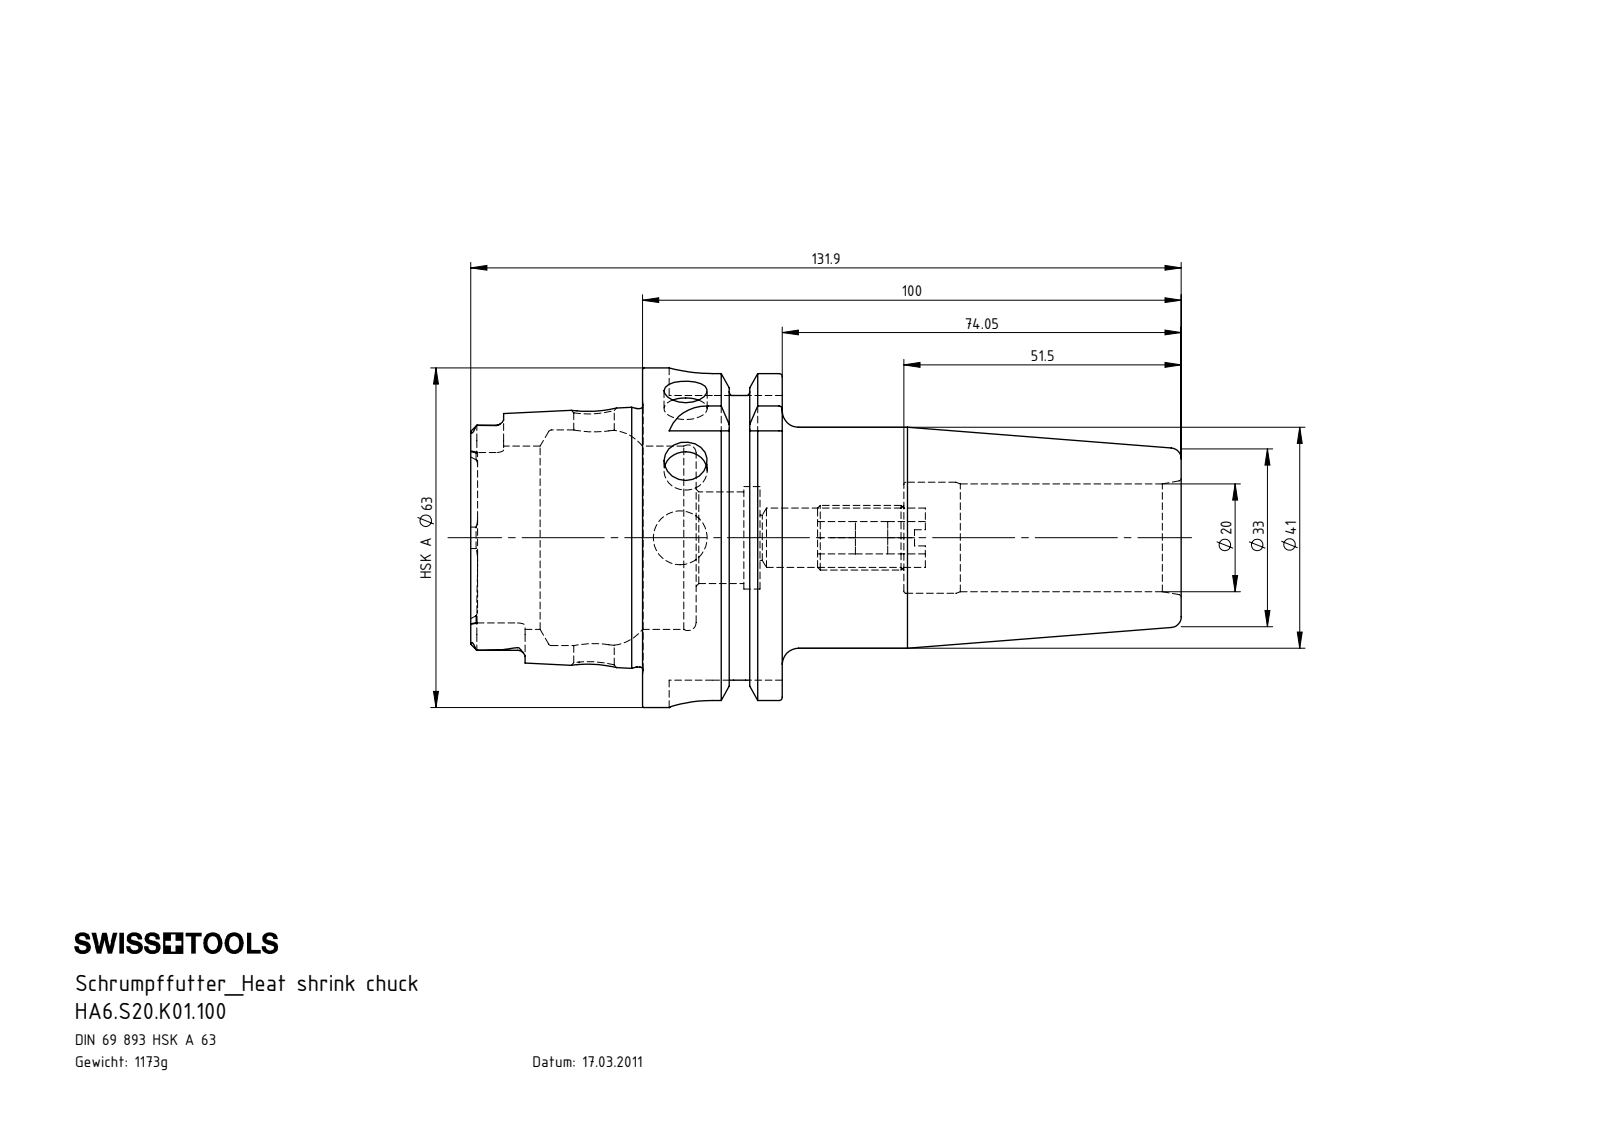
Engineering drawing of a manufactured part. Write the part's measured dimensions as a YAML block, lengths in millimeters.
part_name: "HA6-S20.K01.100; ERU-AN5.K01.020_A; HA6-S20.K01.100_B_Fertigbearbeitung"
step_written_by: "SolidWorks 2012 (AUTOMOTIVE_DESIGN)"
units: millimeters
bodies: {solids: 2, faces: 232, planar: 82, cylindrical: 61, other: 89}
overall_size: [131.9, 63, 63]
volume: 149366
surface_area: 35920
round_holes:
  - {diameter: 8, count: 2}
  - {diameter: 6, count: 1}
  - {diameter: 7.5, count: 1}
  - {diameter: 8.4, count: 1}
  - {diameter: 10, count: 1}
  - {diameter: 11, count: 1}
  - {diameter: 17, count: 1}
  - {diameter: 19, count: 1}
  - {diameter: 20, count: 1}
  - {diameter: 20.6, count: 1}
  - {diameter: 34, count: 1}
  - {diameter: 40, count: 1}
round_bosses_or_shafts:
  - {diameter: 63, count: 1}
  - {diameter: 54.95, count: 1}
  - {diameter: 47.94, count: 1}
  - {diameter: 41, count: 1}
  - {diameter: 12, count: 1}
partial_cylinders:
  - {radius: 1.4, count: 6}
  - {radius: 2.88, count: 4}
  - {radius: 8, count: 4}
face_to_face_distances: [25.95, 16, 9.95, 31.9, 41.85, 57.85, 52.8, 21.8, 131.9, 100]
